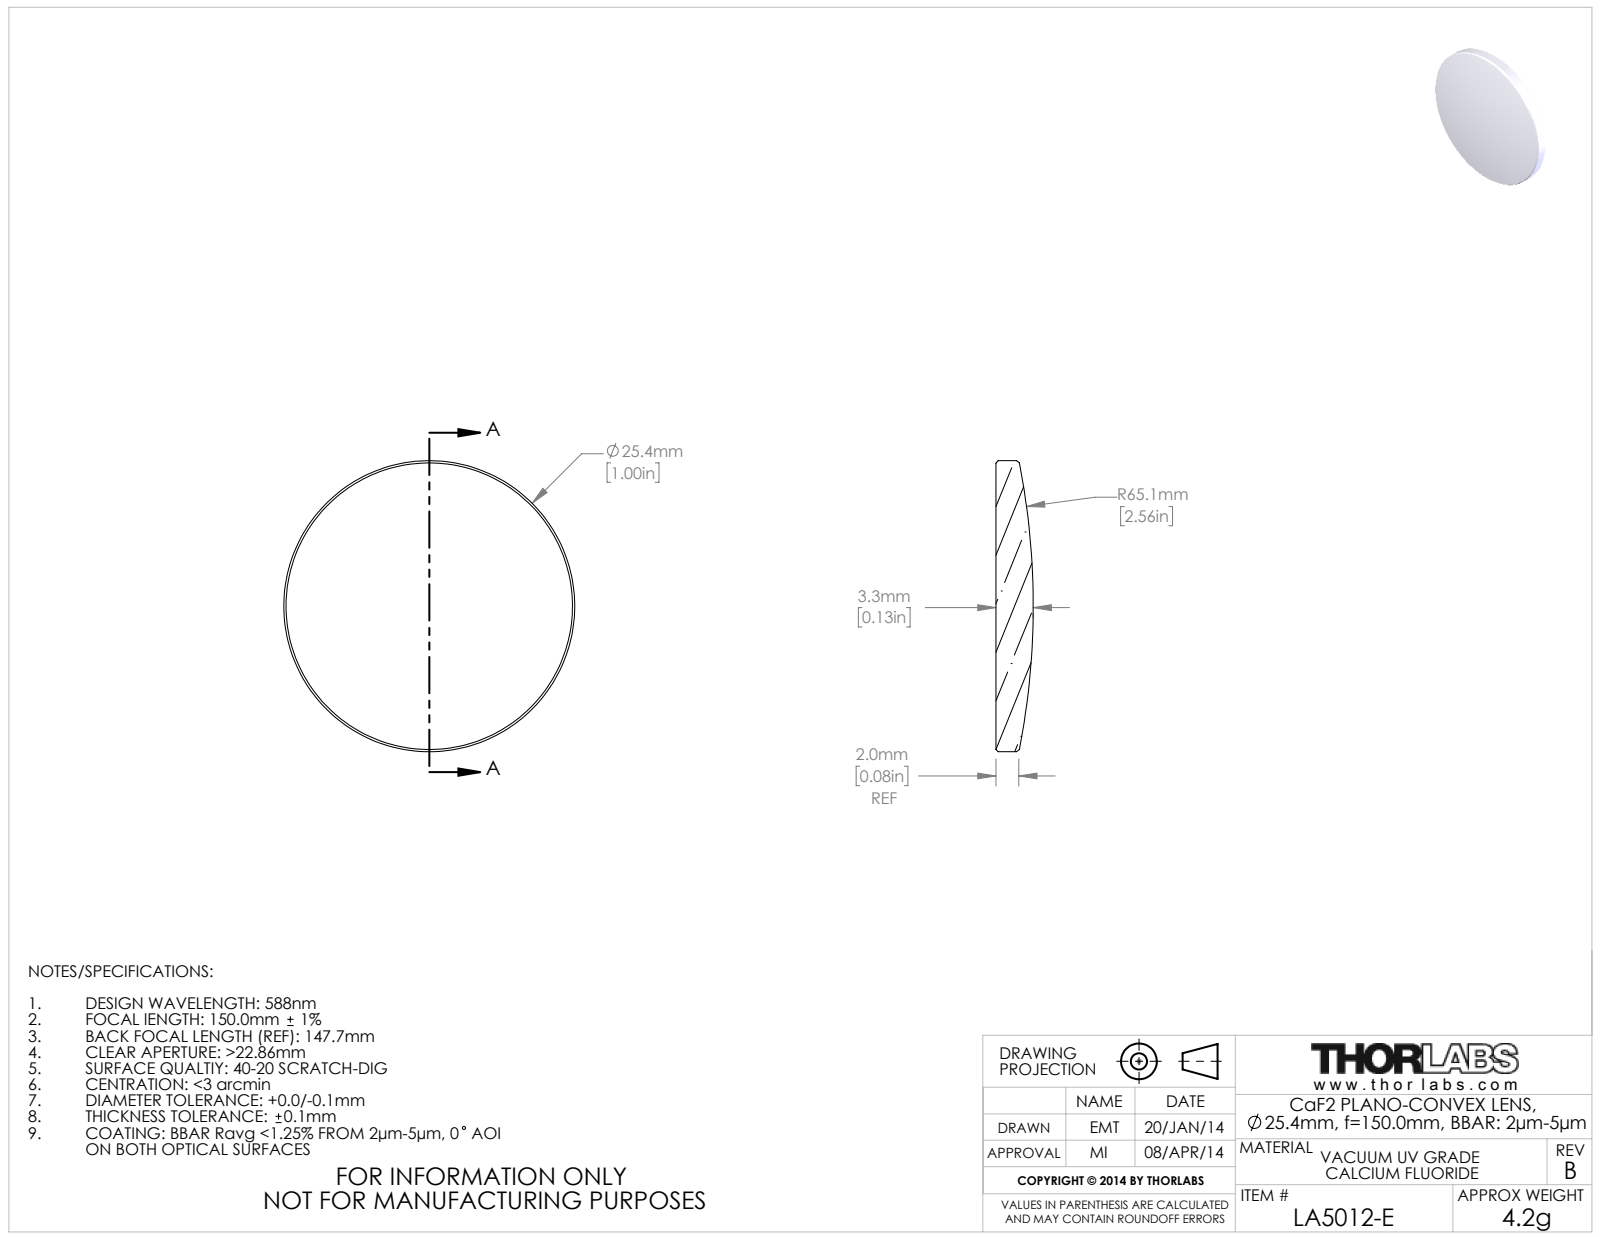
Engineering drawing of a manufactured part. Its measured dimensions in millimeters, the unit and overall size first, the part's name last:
Units: millimetres
Overall size (bounding box): 25.4 × 25.4 × 3.25
Round bosses / shafts (diameter × count): ⌀25.4 ×1
Volume: 1 328 mm³ · Surface area: 1 161 mm²
Bodies: 1 solid, 9 faces (1 planar, 2 cylindrical, 6 other)
Part name (STEP PRODUCT): 20135-E0W
STEP written by: SolidWorks 2018 (CONFIG_CONTROL_DESIGN)
